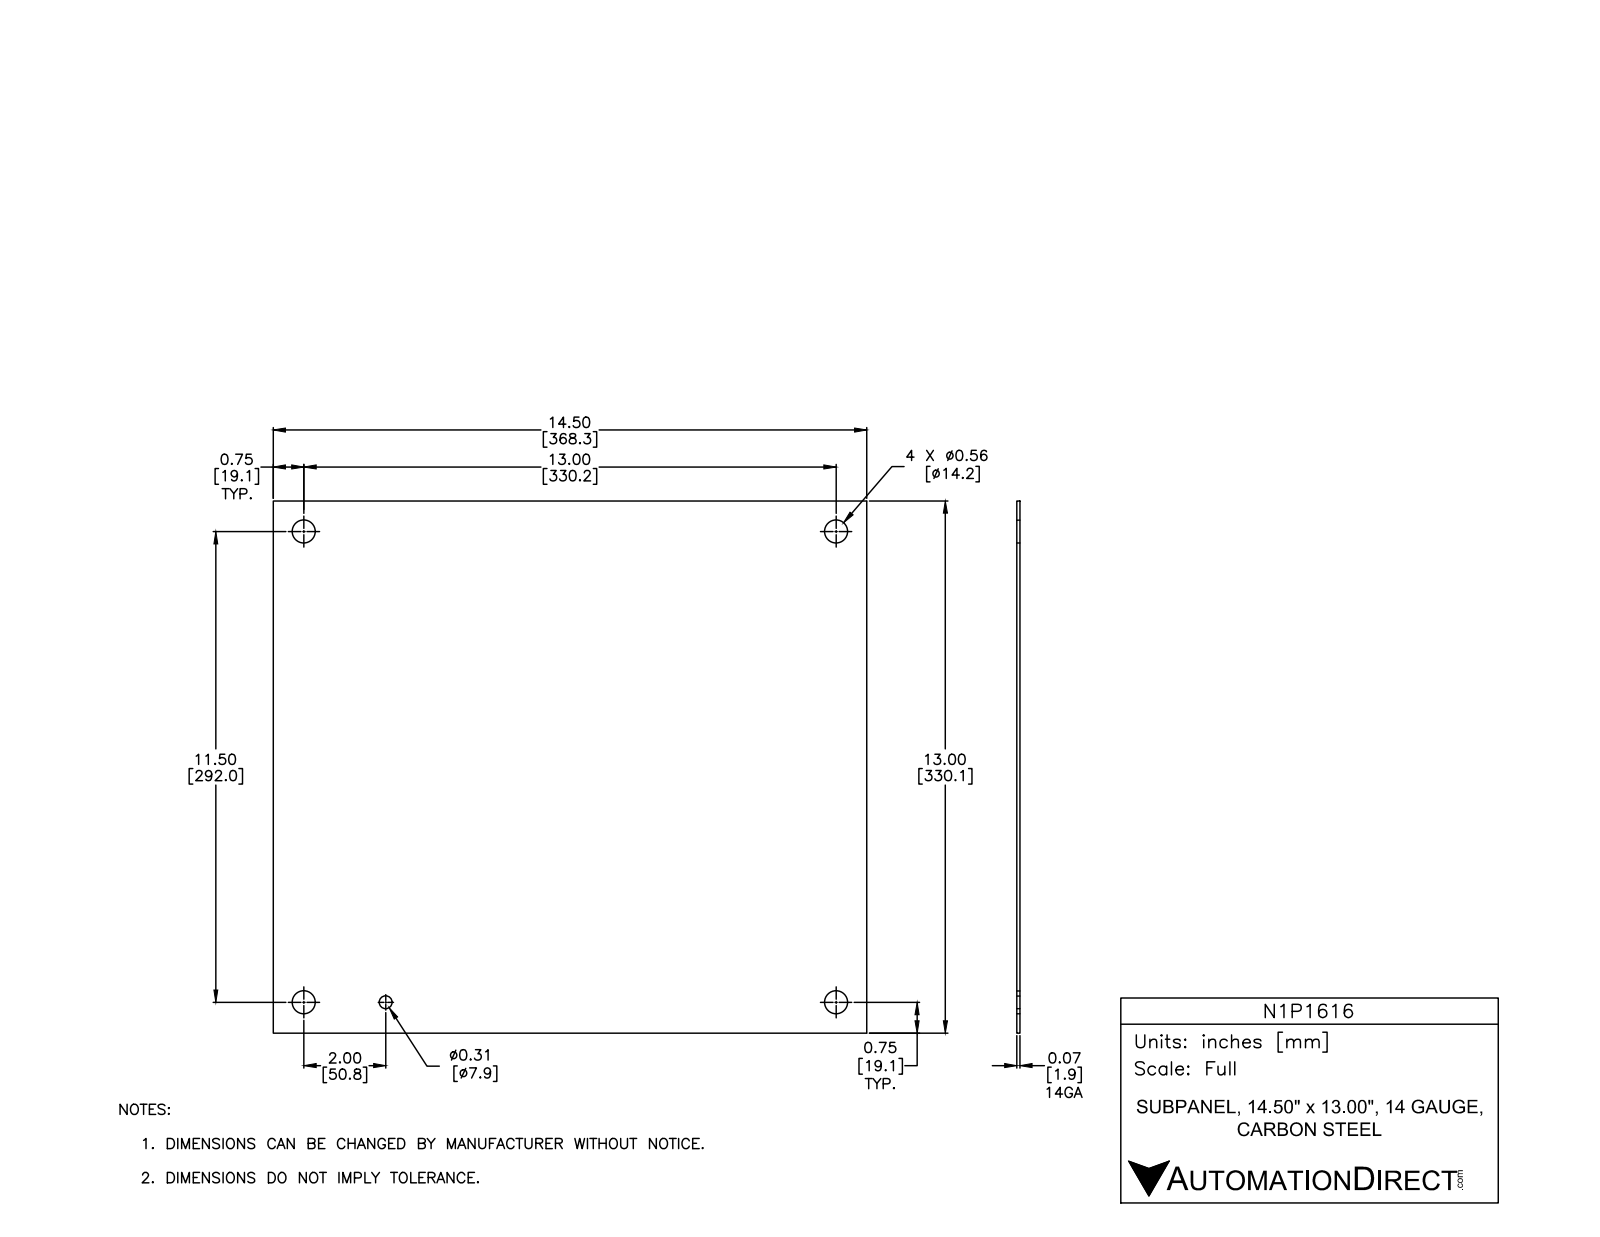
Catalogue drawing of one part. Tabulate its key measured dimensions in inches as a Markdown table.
| quantity | value |
| --- | --- |
| part name | N1P1616-1 |
| STEP written by | Autodesk Inventor 2012 (AUTOMOTIVE_DESIGN) |
| units | inches |
| bodies | 1 solid, 11 faces (6 planar, 5 cylindrical, 0 other) |
| overall size | 14.5 × 13 × 0.074 |
| volume | 13.87 in³ |
| surface area | 379.5 in² |
| round holes (diameter × count) | 0.563 × 4, 0.312 × 1 |
| main face-to-face distances | 0.074, 13, 14.5 |
| hole center spacings | 11.5, 13, 17.357, 2, 11, 11.672, 15.914 |
